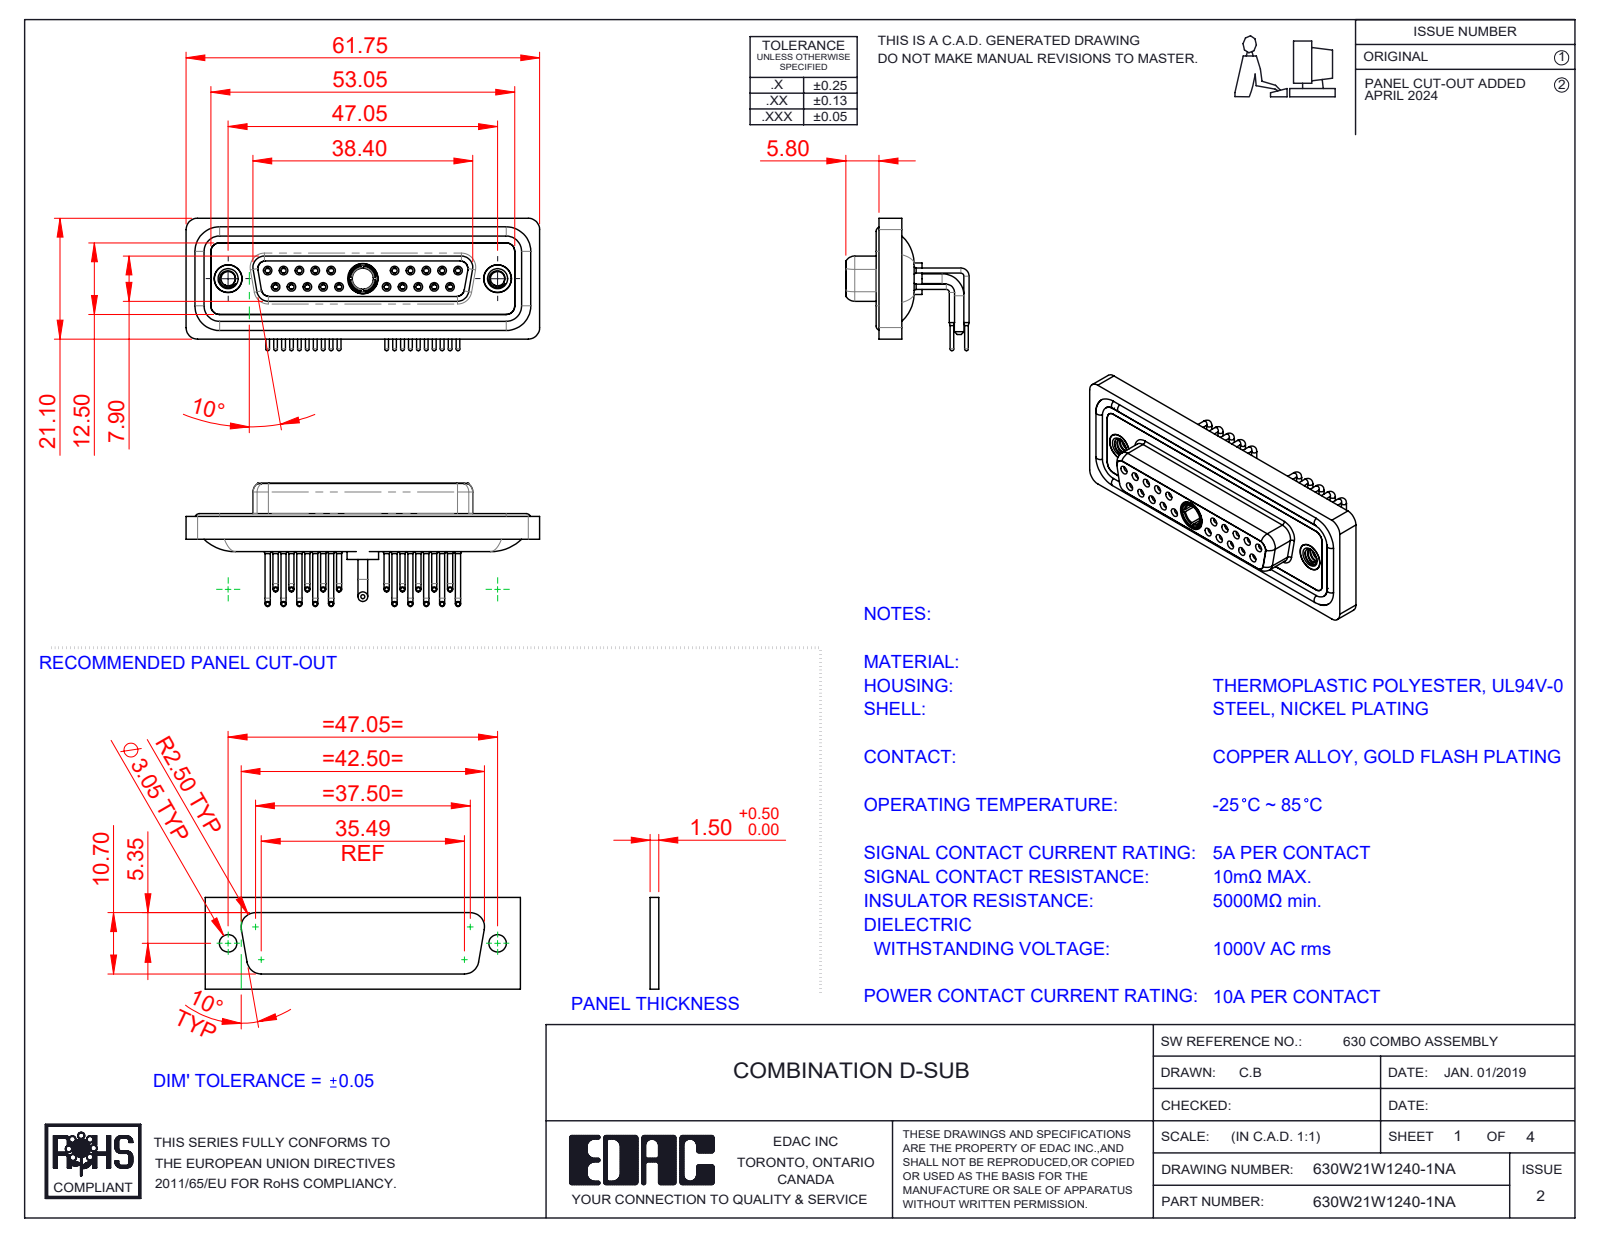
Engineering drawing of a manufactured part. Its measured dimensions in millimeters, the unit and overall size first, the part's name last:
Units: millimetres
Overall size (bounding box): 61.75 × 23.12 × 21.53
Round holes (diameter × count): ⌀0.9 ×20, ⌀1.1 ×20, ⌀1.5 ×20, ⌀2 ×20, ⌀1.6 ×10, ⌀1.7 ×10, ⌀4.85 ×3, ⌀2.5 ×2, ⌀4 ×2, ⌀4.05 ×2, ⌀5 ×2, ⌀3.7 ×1
Round bosses / shafts (diameter × count): ⌀0.9 ×20, ⌀0.65 ×20, ⌀1.6 ×14, ⌀4.95 ×2, ⌀4.8 ×2, ⌀1.7 ×2, ⌀5.5 ×1, ⌀5.2 ×1
Partial cylindrical surfaces — rounded edges, fillets, slot ends (radius × count): R1.5 ×18, R2 ×18, R1.35 ×8, R1.6 ×8, R0.25 ×4, R0.5 ×4, R0.6 ×4, R0.65 ×4
Main face-to-face distances: 0.4, 1.8, 4.1, 1.6, 1.1, 2.5, 1.5, 3.1, 9.8, 0.45
Hole centre spacings: 3.16, 2.77, 5.54, 8.31, 5.04, 19.39, 20.97, 22.16
Volume: 8 440 mm³ · Surface area: 14 732 mm²
Bodies: 29 solids, 1518 faces (434 planar, 671 cylindrical, 413 other)
Part name (STEP PRODUCT): 630W21W1240-1NA; 630Combo Threaded Rivet_A; 630Combo Contact Row 1_50 Contacts; 630Combo Contact Row 2_50 Contacts (+5 more)
STEP written by: SolidWorks 2023 (CONFIG_CONTROL_DESIGN)
